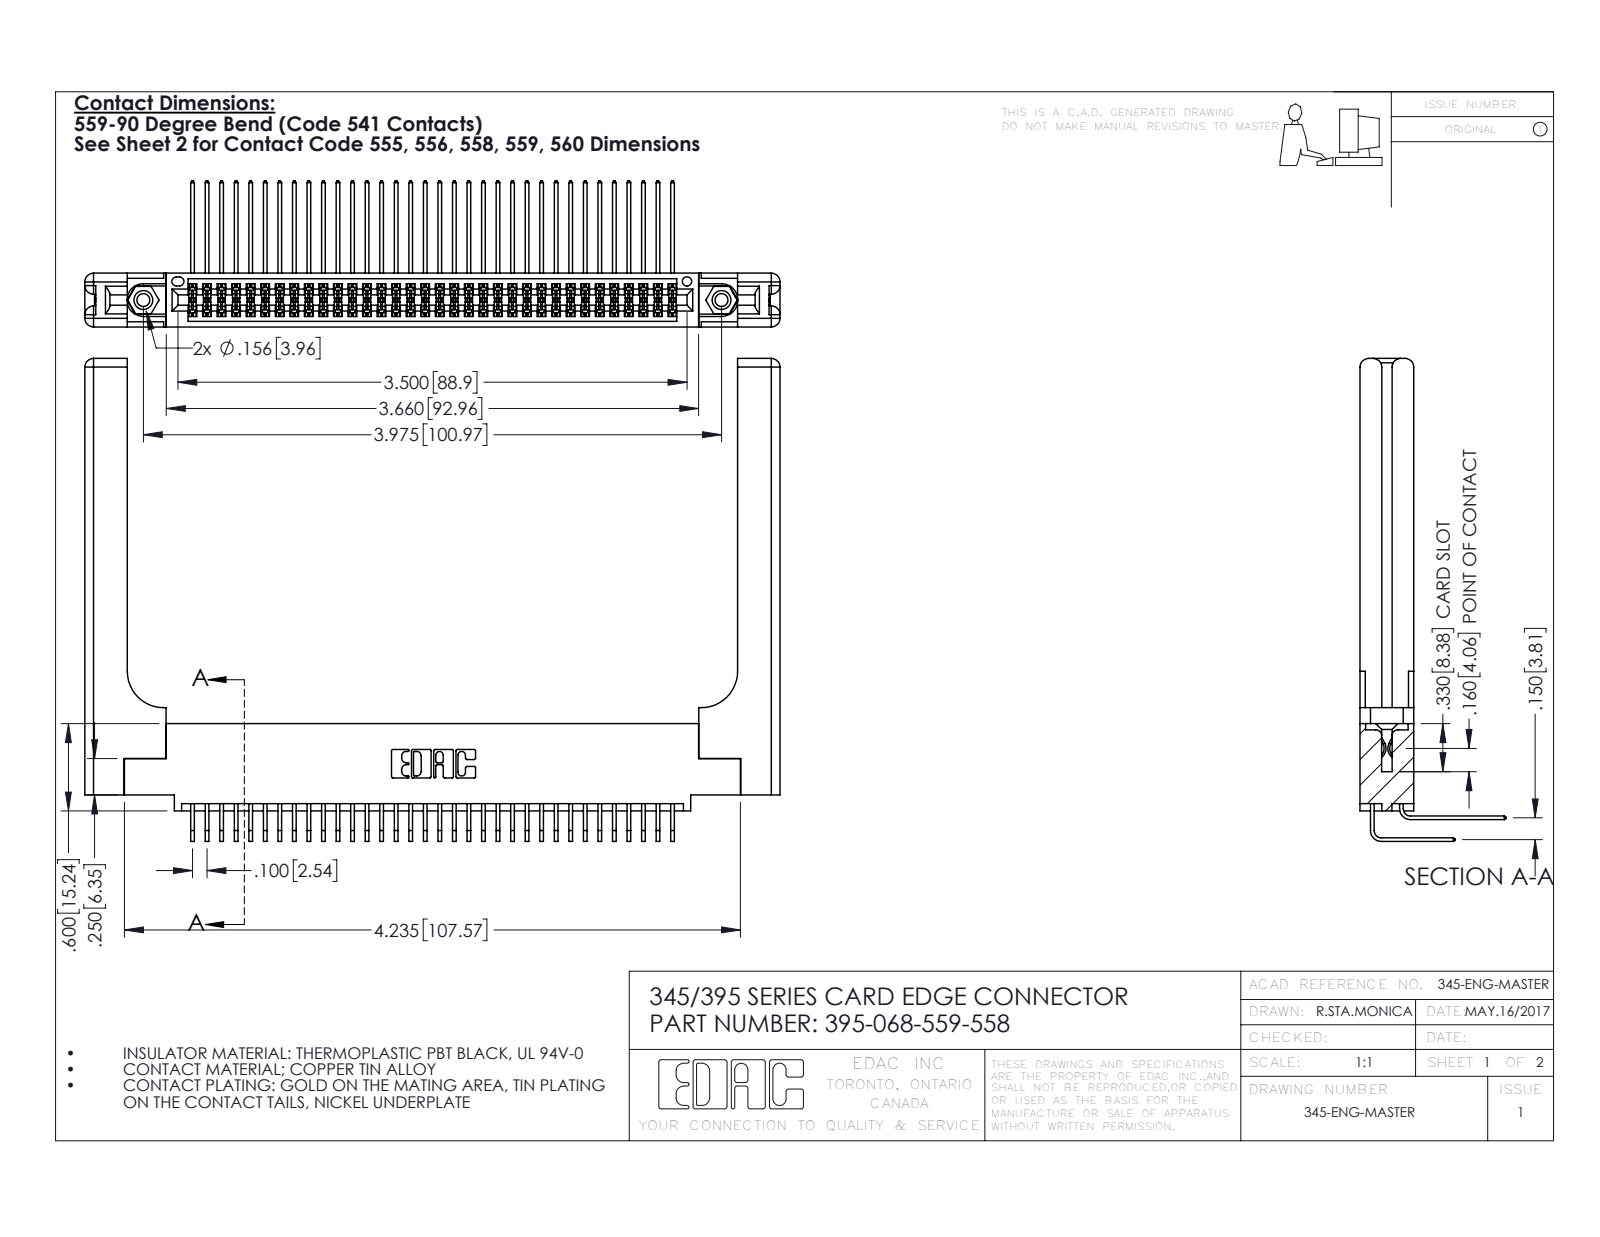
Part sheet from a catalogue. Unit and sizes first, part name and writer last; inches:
Units: inches
Overall size (bounding box): 4.779 × 3.319 × 1.005
Round holes (diameter × count): ⌀0.089 ×2, ⌀0.125 ×2, ⌀0.156 ×2, ⌀0.064 ×1
Round bosses / shafts (diameter × count): ⌀0.155 ×2
Partial cylindrical surfaces — rounded edges, fillets, slot ends (radius × count): R0.006 ×103, R0.01 ×22, R0.06 ×16, R0.007 ×6, R0.031 ×6, R0.026 ×3, R0.014 ×2, R0.019 ×2
Main face-to-face distances: 0.072, 0.37, 0.298, 0.2, 0.098, 0.272, 0.025, 0.225, 0.148, 0.15
Hole centre spacings: 0.27, 3.74, 3.975
Volume: 1.252 in³ · Surface area: 38.18 in²
Bodies: 73 solids, 3922 faces (2612 planar, 1250 cylindrical, 60 other)
Part name (STEP PRODUCT): 345-292-001_559 Tail - 2; 345 Part_0.110 Offset - 0.156 Dia-TH; 345-220-058_345-220-058; 395-068-559-558 (+2 more)
STEP written by: SolidWorks 2016 (CONFIG_CONTROL_DESIGN)
